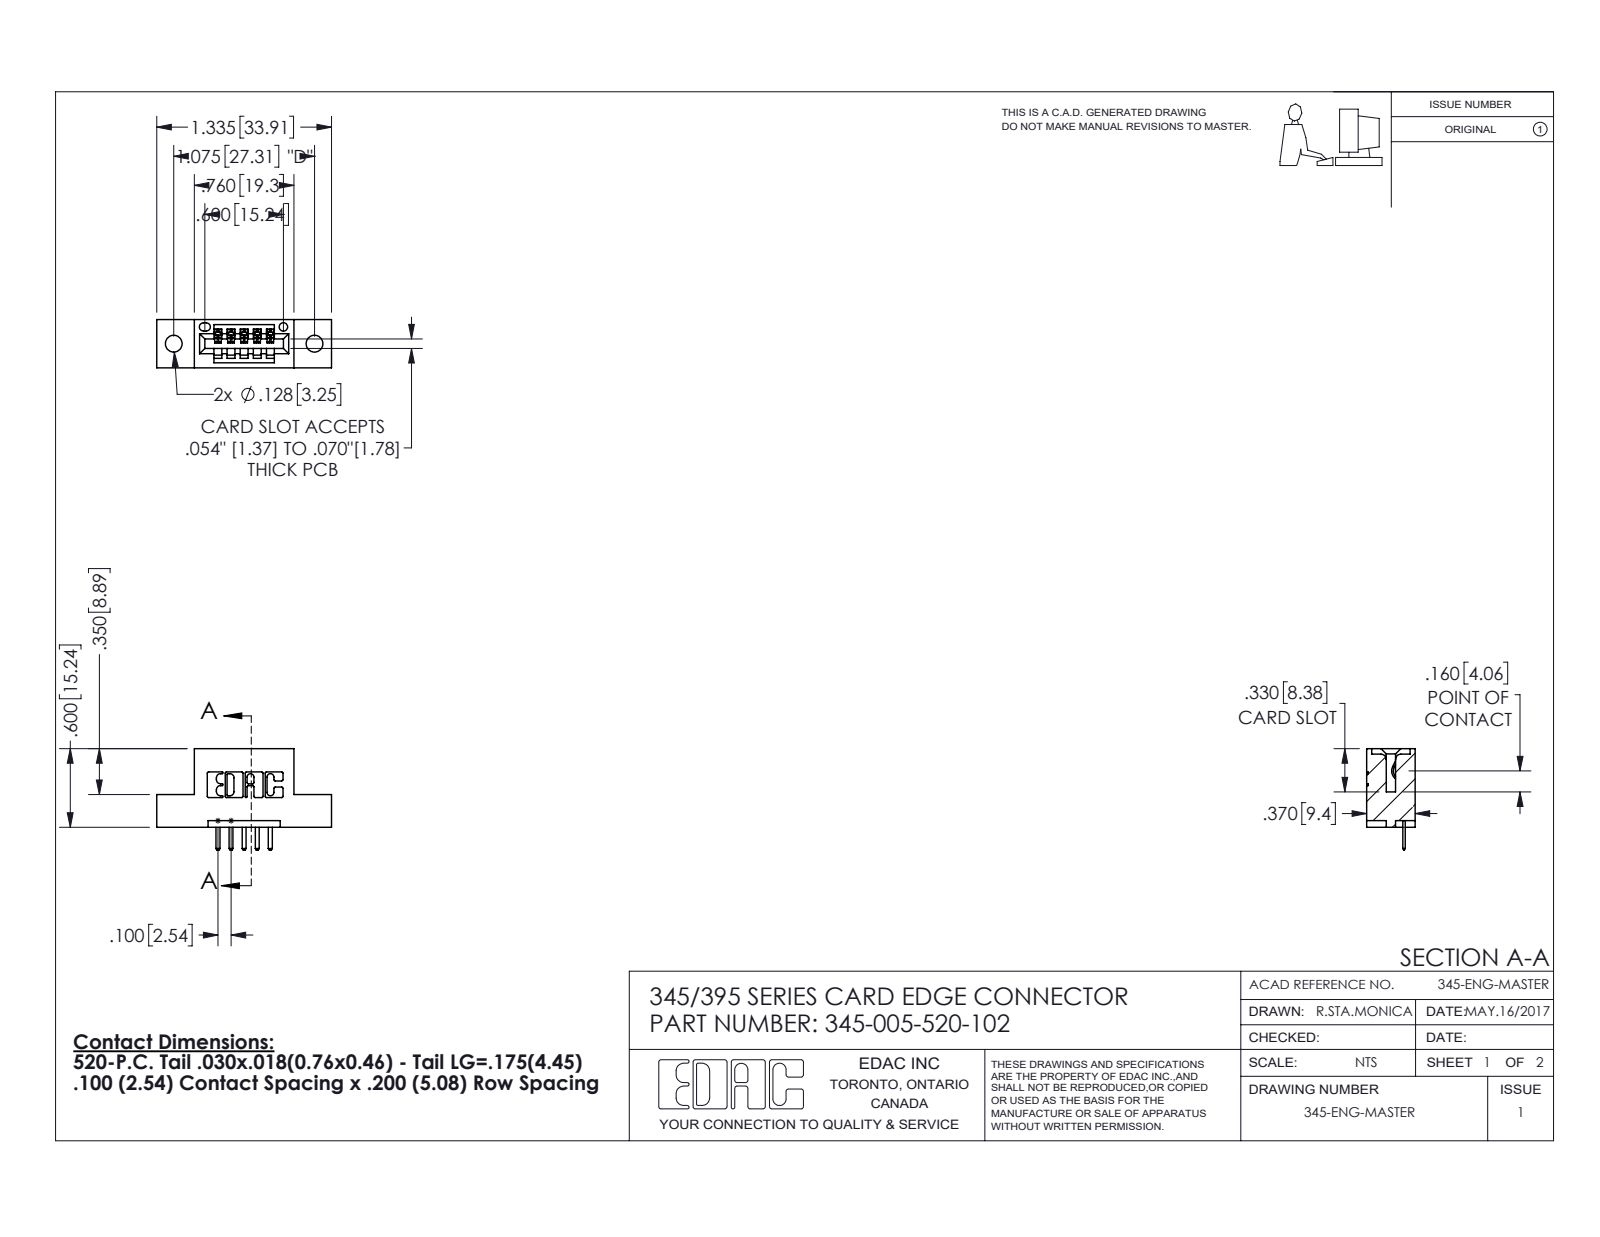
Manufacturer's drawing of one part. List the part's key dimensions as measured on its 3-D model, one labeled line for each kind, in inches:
Part name (STEP PRODUCT): 345 Part_Flush Mounting Lugs - 0.128 Dia; 345-005-520-102; 345-292-001_345-293-120
STEP written by: SolidWorks 2016 (CONFIG_CONTROL_DESIGN)
Units: inches
Bodies: 6 solids, 436 faces (290 planar, 146 cylindrical, 0 other)
Overall size (bounding box): 1.335 × 0.775 × 0.37
Volume: 0.175 in³ · Surface area: 4.631 in²
Round holes (diameter × count): ⌀0.128 ×2, ⌀0.064 ×1
Partial cylindrical surfaces — rounded edges, fillets, slot ends (radius × count): R0.01 ×22, R0.01 ×12, R0.006 ×10, R0.007 ×6, R0.031 ×6, R0.026 ×3, R0.031 ×2, R0.04 ×2
Main face-to-face distances: 0.2, 0.37, 0.1, 0.298, 0.072, 0.25, 0.06, 0.025, 0.55, 0.35
Hole centre spacings: 0.27, 0.847, 1.075
